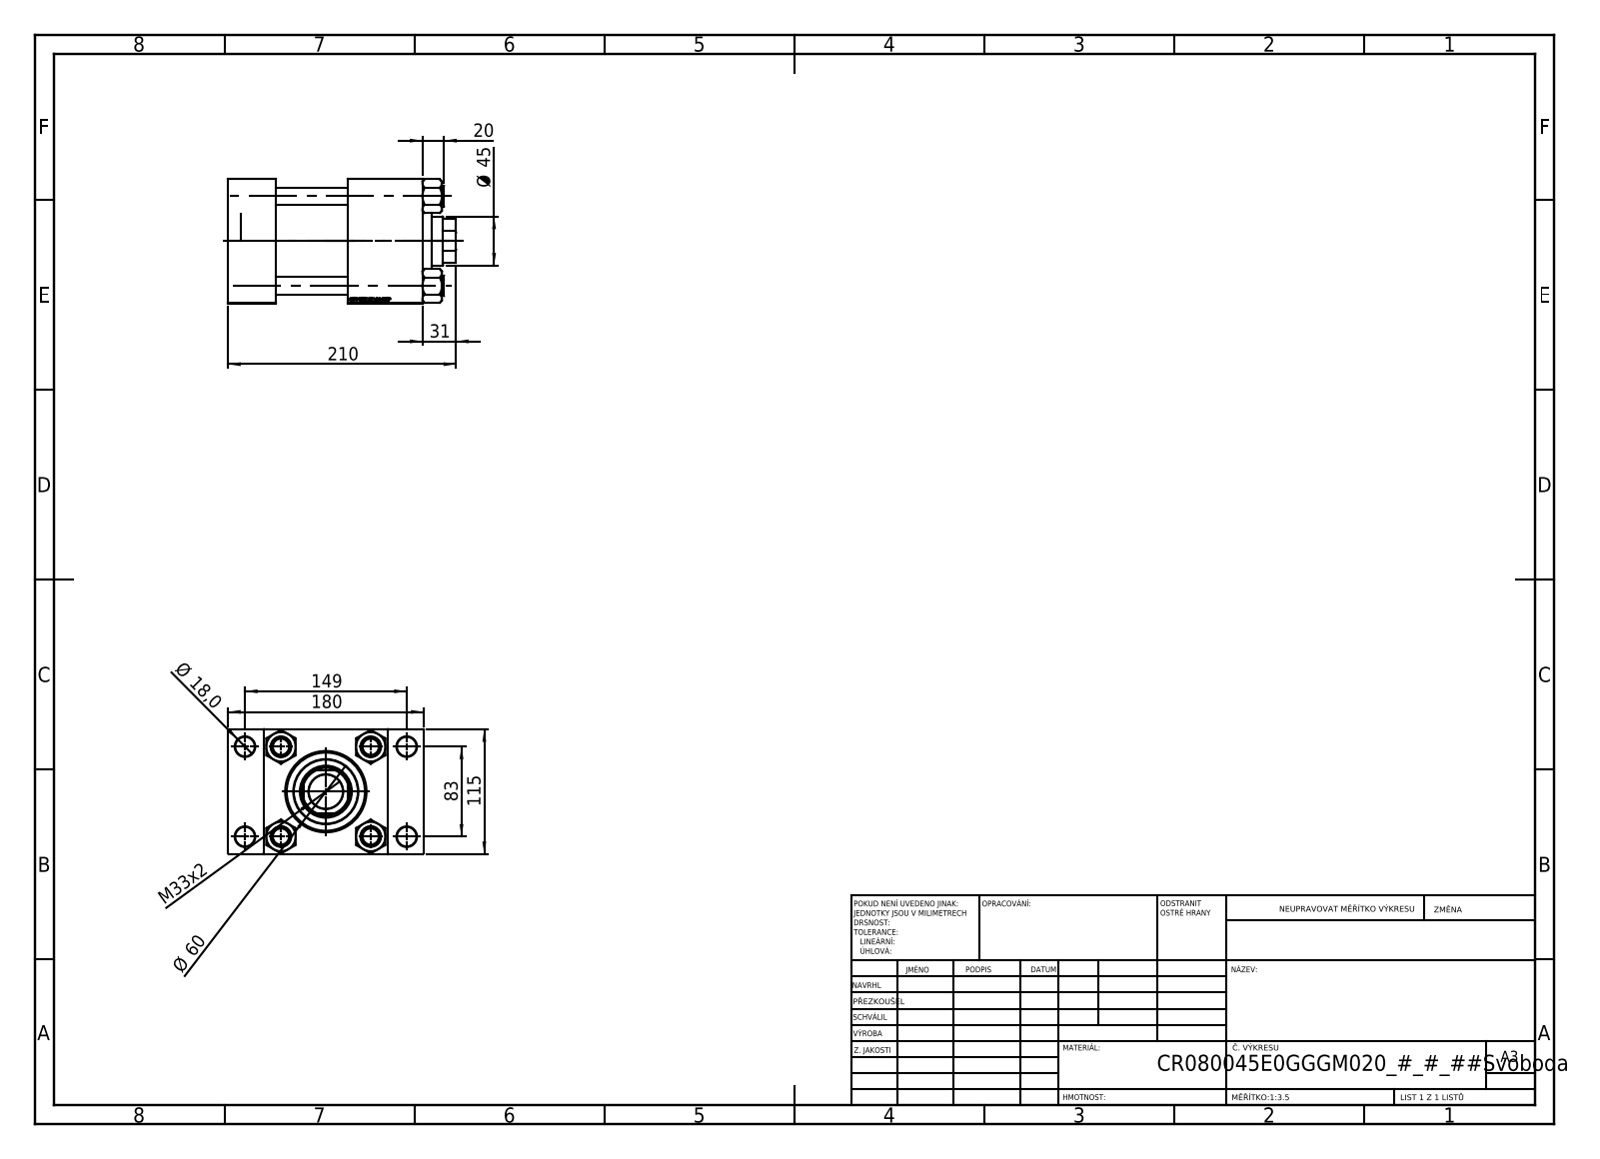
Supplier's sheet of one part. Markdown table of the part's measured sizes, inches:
| quantity | value |
| --- | --- |
| part name | NUT_M5_E; V215CR_VCP_E; V215CR_TYCINKA_E; V215CR_E_Body (+1 more) |
| STEP written by | SolidWorks 2019 (CONFIG_CONTROL_DESIGN) |
| units | inches |
| bodies | 11 solids, 1185 faces (546 planar, 87 cylindrical, 552 other) |
| overall size | 8.268 × 7.087 × 4.528 |
| volume | 129.3 in³ |
| surface area | 488.2 in² |
| round holes (diameter × count) | 0.63 × 4, 0.709 × 4, 0.276 × 2, 1.041 × 2, 1.378 × 2, 1.24 × 1, 1.772 × 1, 1.89 × 1, 2.402 × 1, 2.835 × 1, 3.15 × 1 |
| round bosses / shafts (diameter × count) | 0.748 × 4, 3.386 × 1, 2.362 × 1 |
| partial cylindrical surfaces (radius × count) | 0.866 × 1 |
| main face-to-face distances | 4.528, 1.732, 7.047, 5.315, 1.28, 5.807, 4.331, 2.598, 2.717, 7.087 |
| hole center spacings | 1.305, 2.302, 3.256, 3.357, 3.513, 4.561, 5.607, 3.268 |
